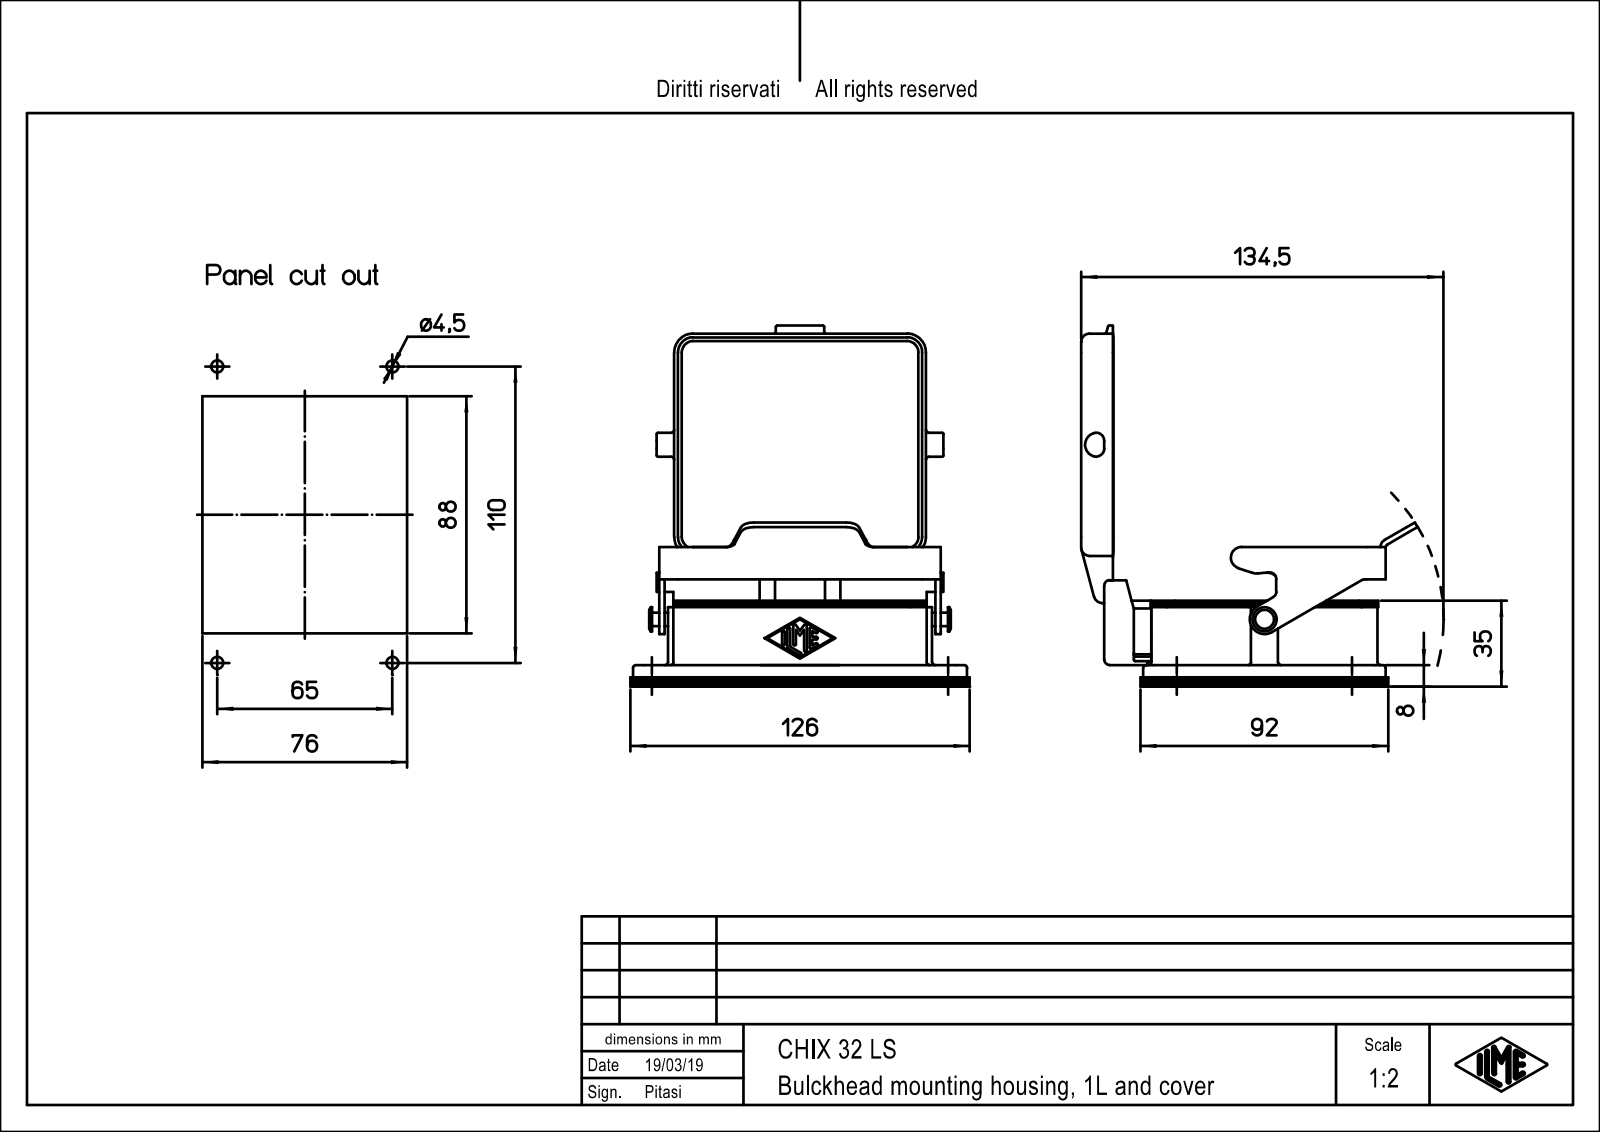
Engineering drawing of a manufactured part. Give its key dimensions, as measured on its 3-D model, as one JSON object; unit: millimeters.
{"part_name": "CHIX_32_L; CHIX_32_LS.stp", "step_written_by": "PTC Creo Elements/Direct Modeling 19.0E 27-Jun-2016 (C) Parametric Technology GmbH (AUTOMOTIVE_DESIGN)", "units": "millimeters", "bodies": {"solids": 1, "faces": 357, "planar": 198, "cylindrical": 139, "other": 20}, "overall_size": [134.35, 134, 126], "volume_mm3": 112857, "surface_area_mm2": 74370, "round_holes": [[3.1, 8], [4.4, 4], [4.5, 4], [4.2, 1]], "round_bosses_or_shafts": [[9, 1], [6, 1], [5, 1]], "partial_cylinders_radius": [[3, 14], [1.5, 9], [5, 8], [6, 8], [2, 7], [0.5, 6], [7, 6], [4, 5]], "face_to_face_distances": [2, 3, 91, 27, 81, 8, 4, 3.25, 29, 3.75], "hole_center_spacings": [16.28, 27, 32.37, 36, 40.41, 66.03, 77.5, 82.07]}
